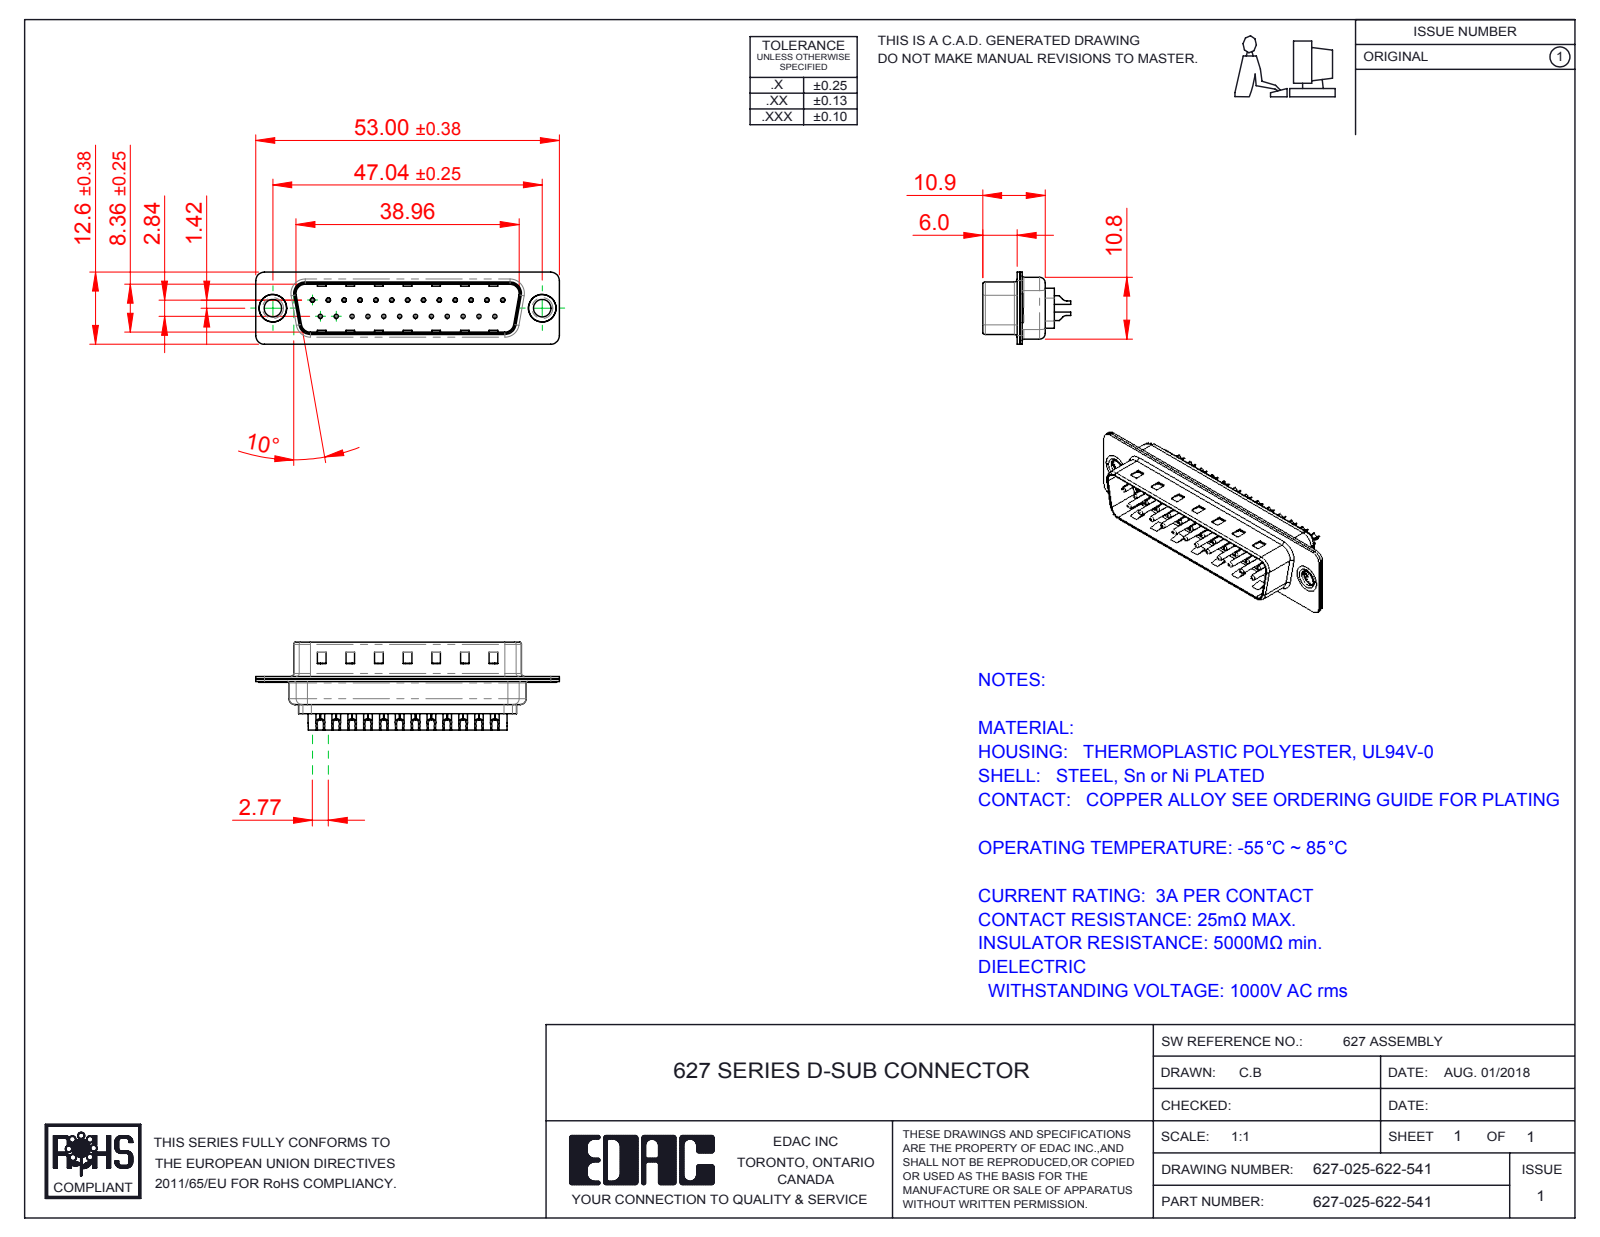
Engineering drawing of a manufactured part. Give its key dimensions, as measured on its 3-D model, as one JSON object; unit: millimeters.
{"part_name": "627 Thru Hole Rivet; 627 Contact Row 2_22L; 627 Housing_25 LP; 627 Shell Rear_25 Contacts (+3 more)", "step_written_by": "SolidWorks 2016 (CONFIG_CONTROL_DESIGN)", "units": "millimeters", "bodies": {"solids": 30, "faces": 1950, "planar": 521, "cylindrical": 846, "other": 583}, "overall_size": [53, 15.35, 12.6], "volume_mm3": 2613, "surface_area_mm2": 7711, "round_holes": [[0.35, 25], [1.1, 25], [1.6, 25], [3.05, 2], [4, 2], [4.8, 2]], "round_bosses_or_shafts": [[2, 25], [1.5, 25], [0.75, 25], [5, 2], [4.9, 2], [3.55, 2]], "partial_cylinders_radius": [[1.5, 16], [2, 12], [0.5, 8], [1.6, 8], [1, 6], [0.25, 4], [0.6, 4], [0.65, 4]], "face_to_face_distances": [0.4, 0.45, 0.82, 9.58, 0.9, 8.76, 1.5, 1.4, 6.5, 6.05], "hole_center_spacings": [3.16, 8.31, 2.77, 5.54, 11.08, 16.62, 5.03, 5.04]}
